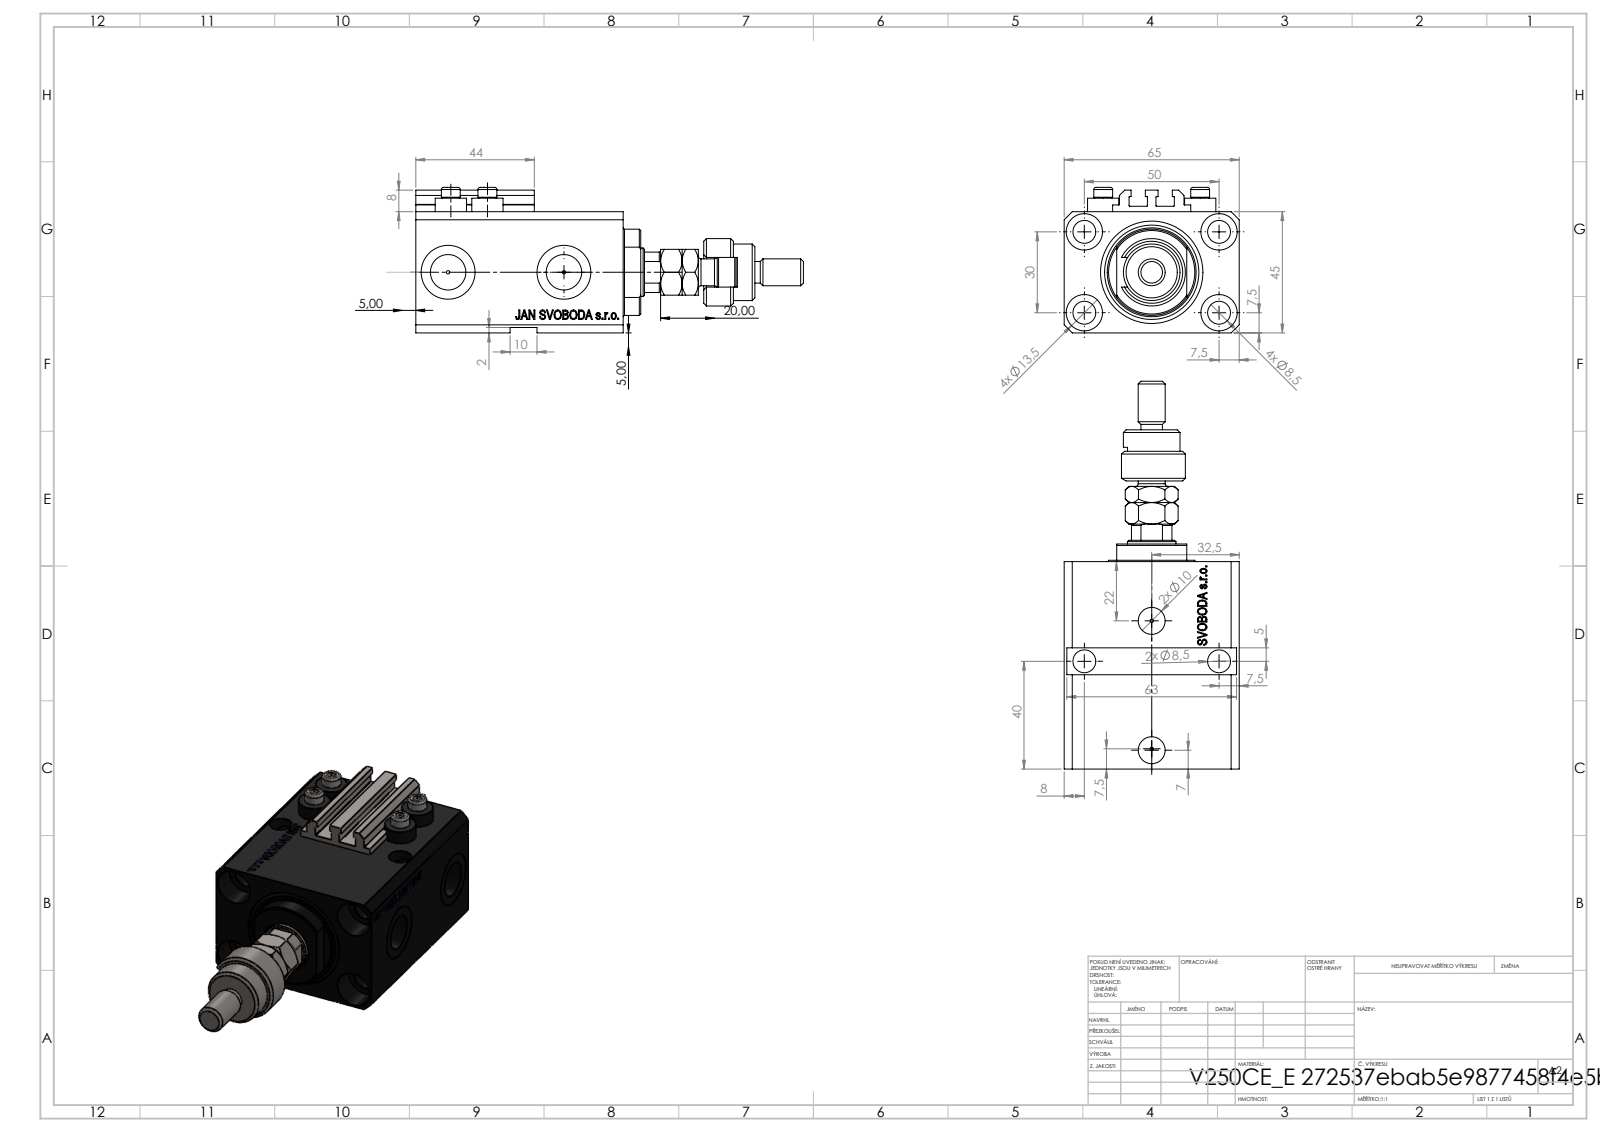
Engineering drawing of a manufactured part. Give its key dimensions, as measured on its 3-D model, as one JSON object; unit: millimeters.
{"part_name": "ALLEN BOLT V250CE; FEMALE_PART_FOR_DFA; V250CE_VC_E; V250CE_E_Body (+2 more)", "step_written_by": "SolidWorks 2019 (CONFIG_CONTROL_DESIGN)", "units": "millimeters", "bodies": {"solids": 10, "faces": 1168, "planar": 543, "cylindrical": 151, "other": 474}, "overall_size": [144, 65, 54], "volume_mm3": 207953, "surface_area_mm2": 65767, "round_holes": [[8.5, 7], [1.25, 4], [4, 4], [13.5, 4], [10, 2], [13.16, 2], [20, 2], [18, 1], [38, 1]], "round_bosses_or_shafts": [[11.6, 4], [7, 4], [25, 1], [21, 1], [16, 1], [10, 1], [8, 1]], "partial_cylinders_radius": [[0.2, 10], [5.5, 1], [8.5, 1], [8.75, 1], [16, 1]], "face_to_face_distances": [45, 14, 65, 63, 77, 2, 3, 5, 6.9, 56.1], "hole_center_spacings": [29.15, 50, 13.6, 15.12, 18.81, 18.97, 26.22, 26.61]}
